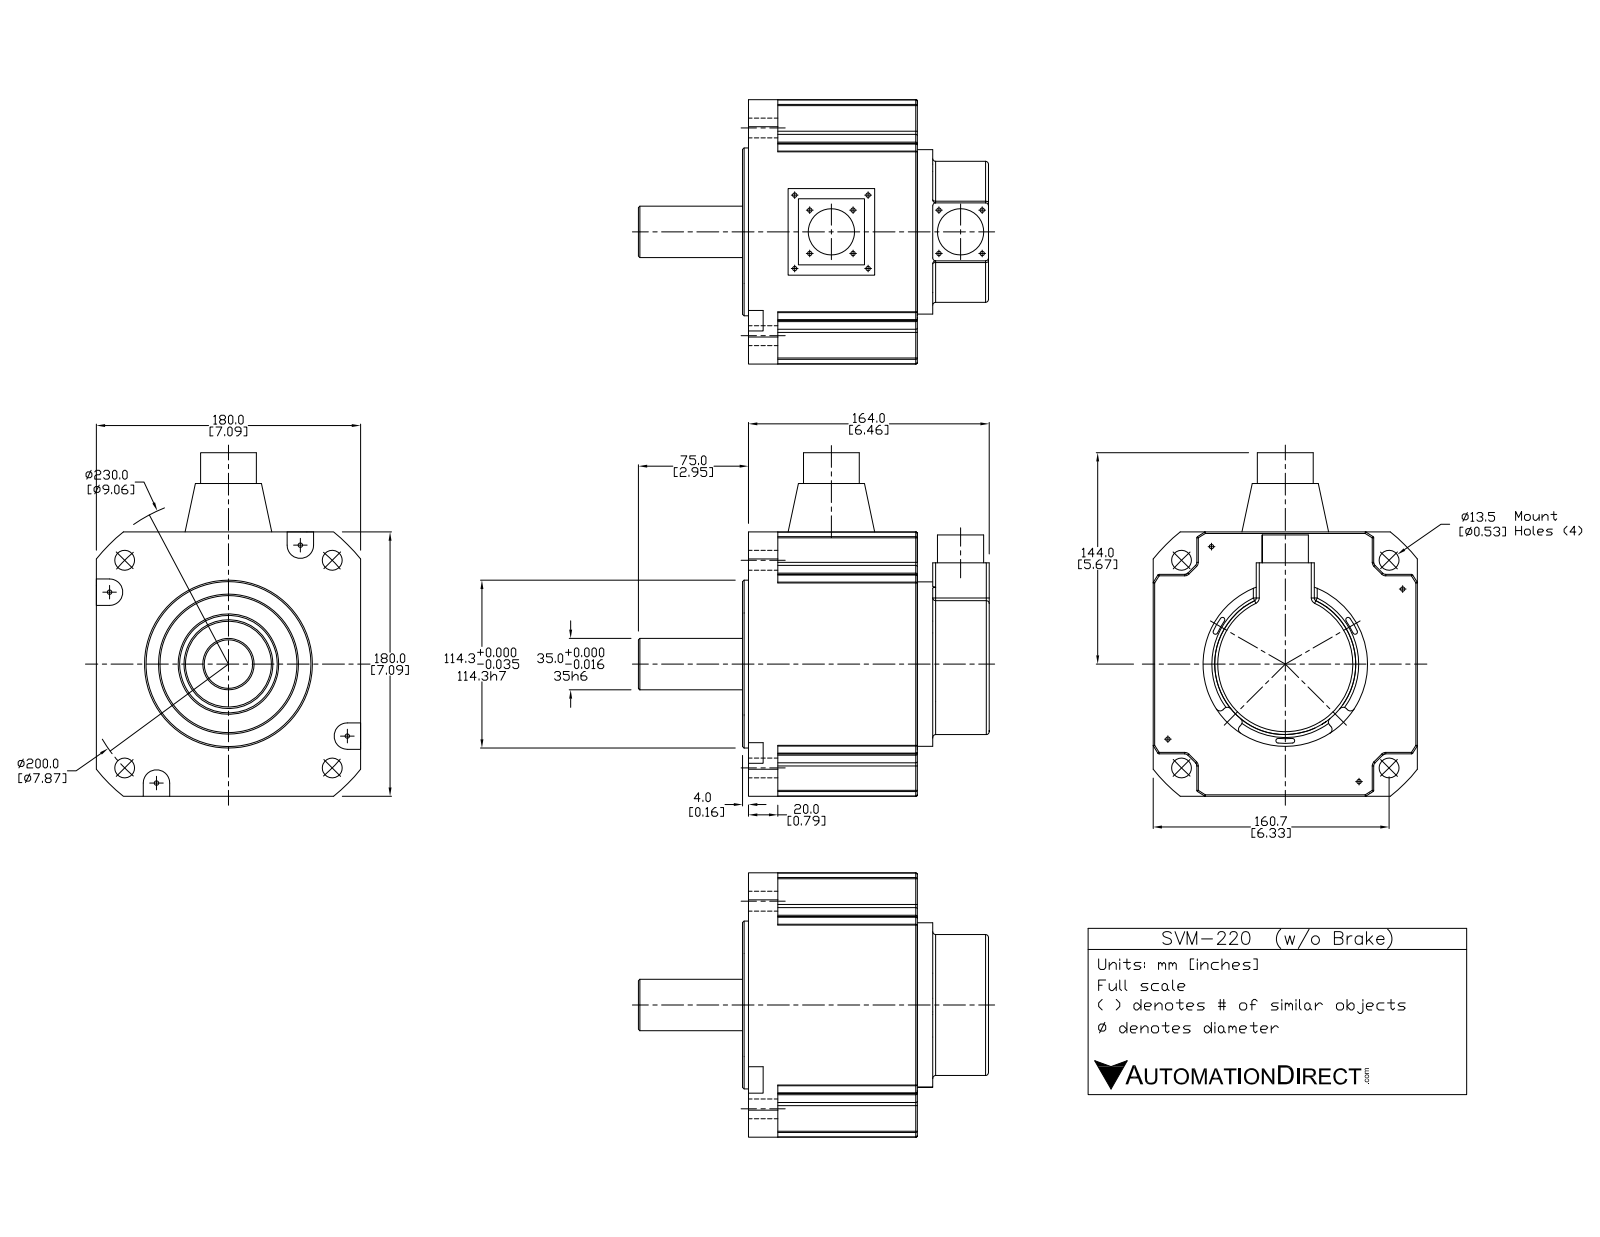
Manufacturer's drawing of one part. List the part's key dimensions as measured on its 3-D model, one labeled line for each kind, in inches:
Part name (STEP PRODUCT): SVM-220
STEP written by: SolidWorks 2015 (AUTOMOTIVE_DESIGN)
Units: inches
Bodies: 32 solids, 460 faces (238 planar, 135 cylindrical, 87 other)
Overall size (bounding box): 9.409 × 9.213 × 7.087
Volume: 239.4 in³ · Surface area: 549 in²
Round holes (diameter × count): ⌀0.531 ×4, ⌀1.063 ×1, ⌀1.311 ×1, ⌀3.701 ×1
Round bosses / shafts (diameter × count): ⌀0.079 ×17, ⌀0.094 ×6, ⌀0.63 ×4, ⌀0.142 ×3, ⌀4.498 ×1, ⌀4.409 ×1, ⌀3.78 ×1, ⌀2.638 ×1
Partial cylindrical surfaces — rounded edges, fillets, slot ends (radius × count): R0.197 ×8, R0.039 ×4, R0.157 ×4, R0.236 ×4, R0.354 ×4, R2.559 ×1, R4.528 ×1
Main face-to-face distances: 2.795, 7.087, 1.219, 3.583, 0.787, 0.709, 0.609, 4.291, 3.504, 0.61
Hole centre spacings: 3.937, 5.568, 7.874, 3.676
